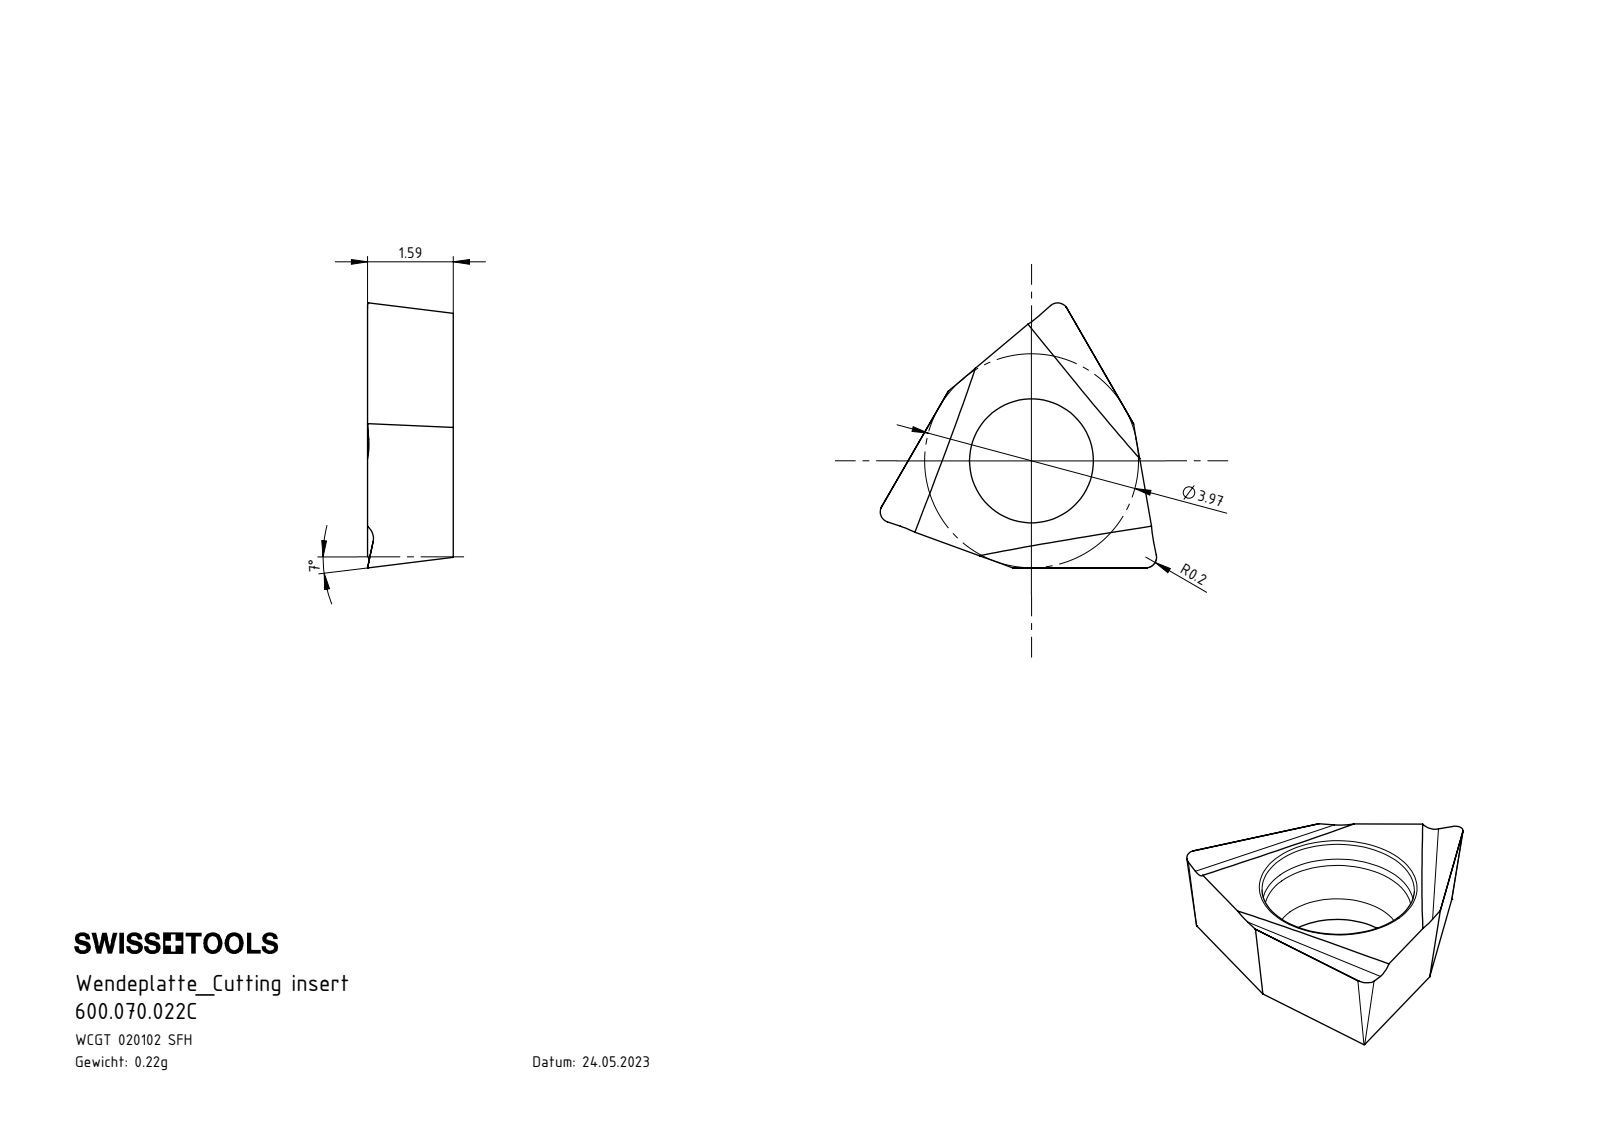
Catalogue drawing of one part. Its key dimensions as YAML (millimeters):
part_name: "600.070.022C"
step_written_by: "SolidWorks 2022 (AUTOMOTIVE_DESIGN)"
units: millimeters
bodies: {solids: 1, faces: 31, planar: 14, cylindrical: 5, other: 12}
overall_size: [5.13, 4.92, 1.59]
volume: 15
surface_area: 56
round_holes:
  - {diameter: 2.3, count: 1}
partial_cylinders:
  - {radius: 0.3, count: 3}
face_to_face_distances: [1.59]
